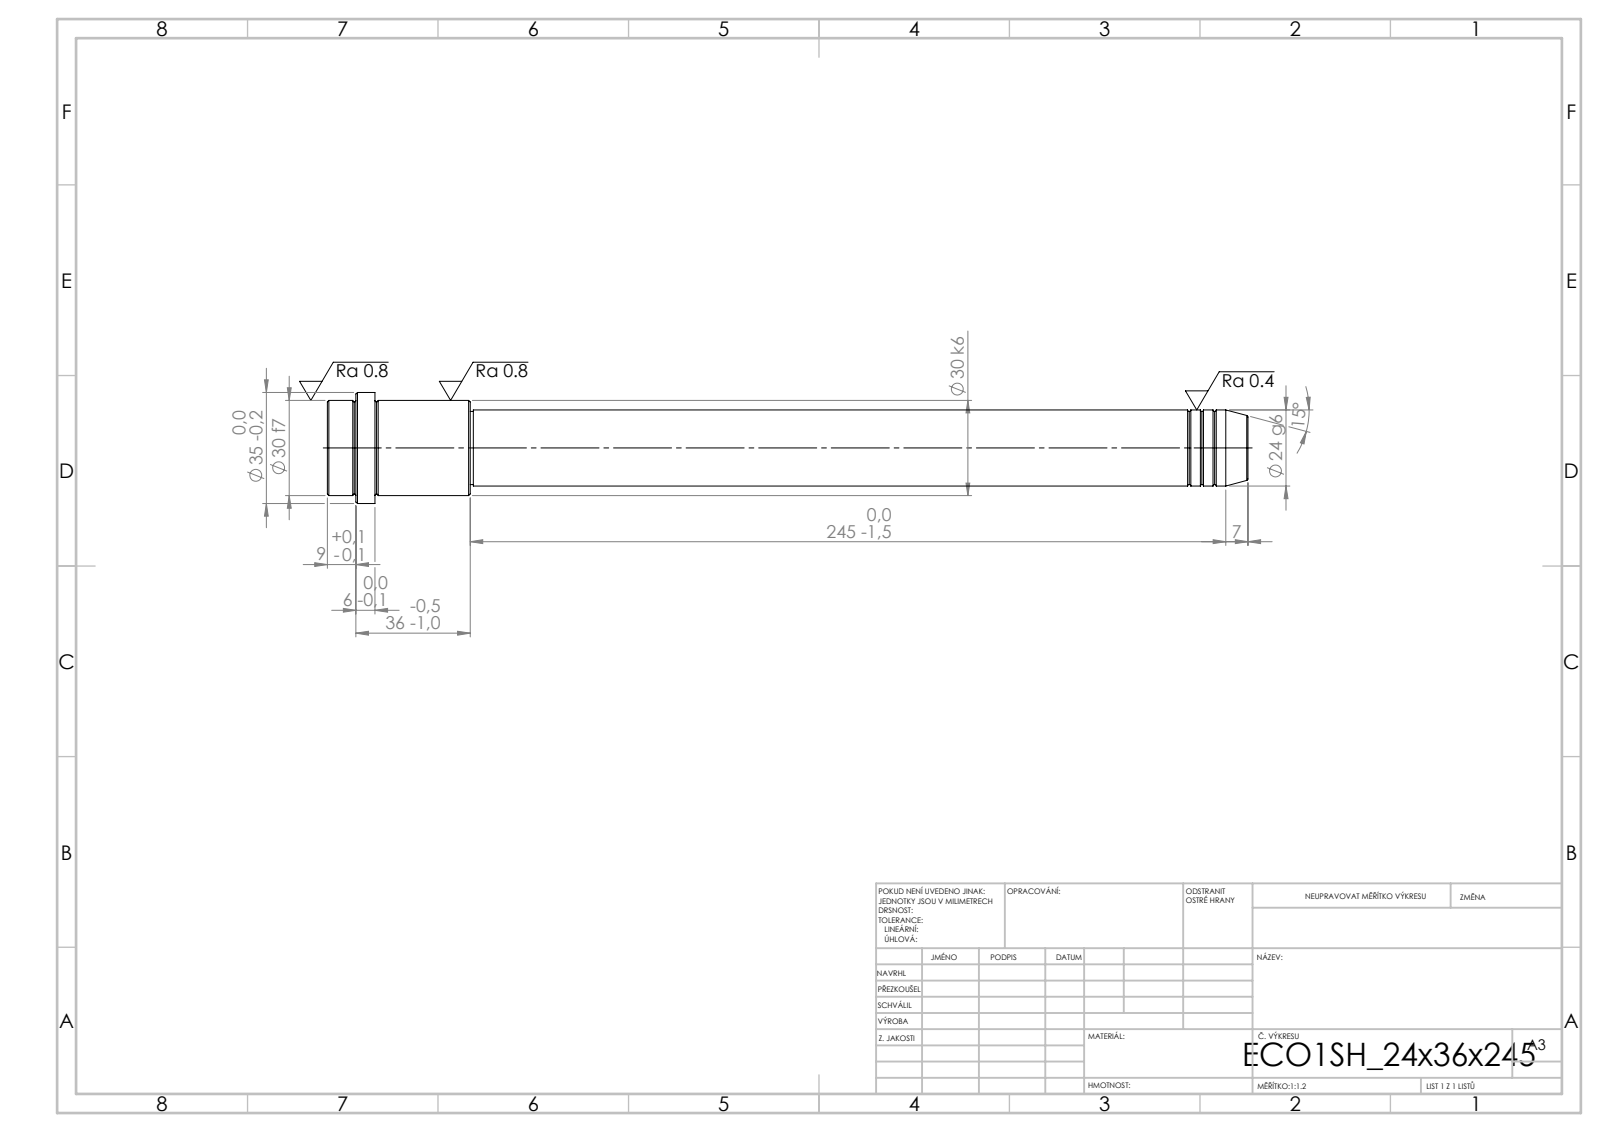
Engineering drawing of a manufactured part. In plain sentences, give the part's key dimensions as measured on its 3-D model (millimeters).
Its 3-D file was written by "SolidWorks 2019 (CONFIG_CONTROL_DESIGN)". It is 1 solid with 52 faces: 6 planar, 16 cylindrical and 30 other. Overall it measures 290 by 35 by 35 millimeters. Its volume is 143 471 cubic millimeters and its surface area 24 774 square millimeters. Round bosses or shafts: 1 of diameter 35, 1 of diameter 30, 1 of diameter 24, 1 of diameter 23. The main face-to-face distances are 290, 275, 15, 245, 30, 45, 281, 36, 6, 9.
